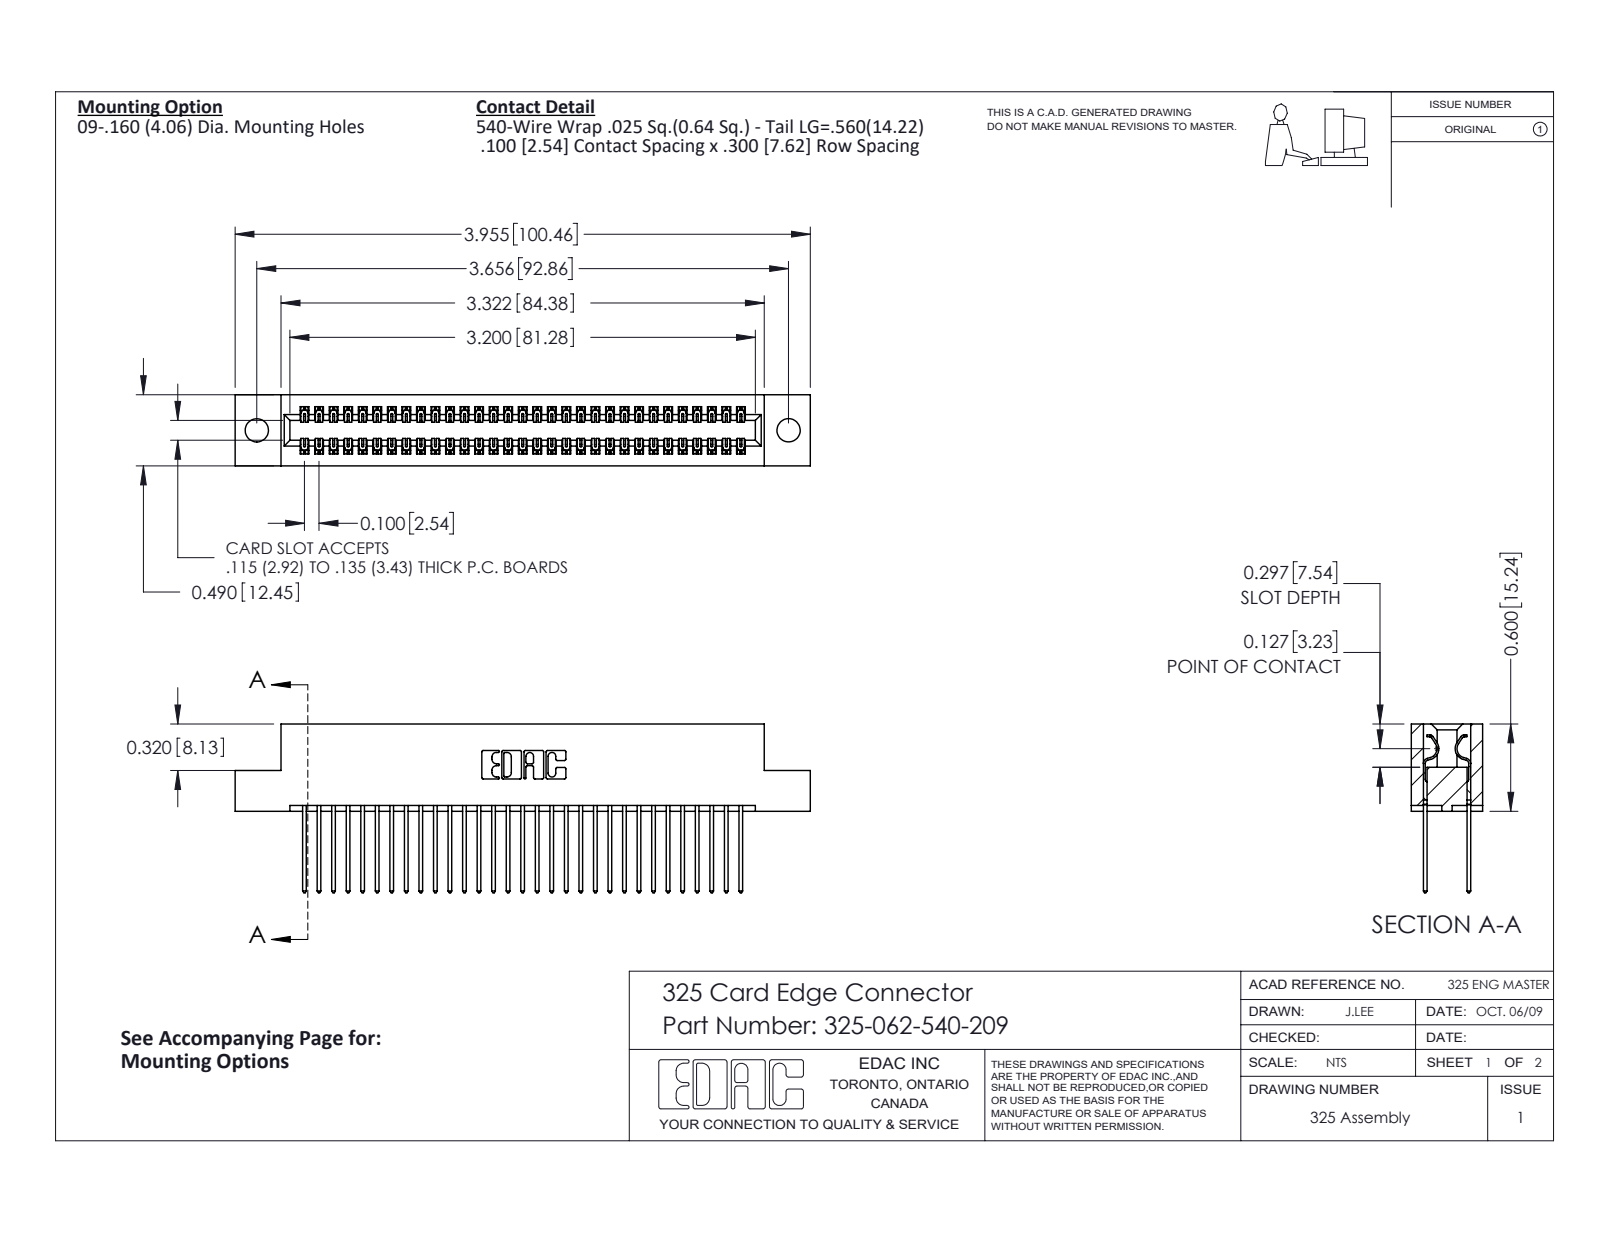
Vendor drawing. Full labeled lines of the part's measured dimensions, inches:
Part name (STEP PRODUCT): 325-062-540-209; 325-292-001_325-293-140; 325 Part_.160 TH
STEP written by: SolidWorks 2016 (CONFIG_CONTROL_DESIGN)
Units: inches
Bodies: 63 solids, 3338 faces (2302 planar, 1036 cylindrical, 0 other)
Overall size (bounding box): 3.955 × 1.16 × 0.49
Volume: 0.786 in³ · Surface area: 25.36 in²
Round holes (diameter × count): ⌀0.16 ×2
Partial cylindrical surfaces — rounded edges, fillets, slot ends (radius × count): R0.006 ×93, R0.01 ×62, R0.01 ×22, R0.007 ×6, R0.031 ×6, R0.026 ×3, R0.014 ×2, R0.022 ×2
Main face-to-face distances: 0.083, 0.407, 0.3, 0.107, 0.383, 0.025, 0.49, 0.325, 0.275, 0.04
Hole centre spacings: 3.656
